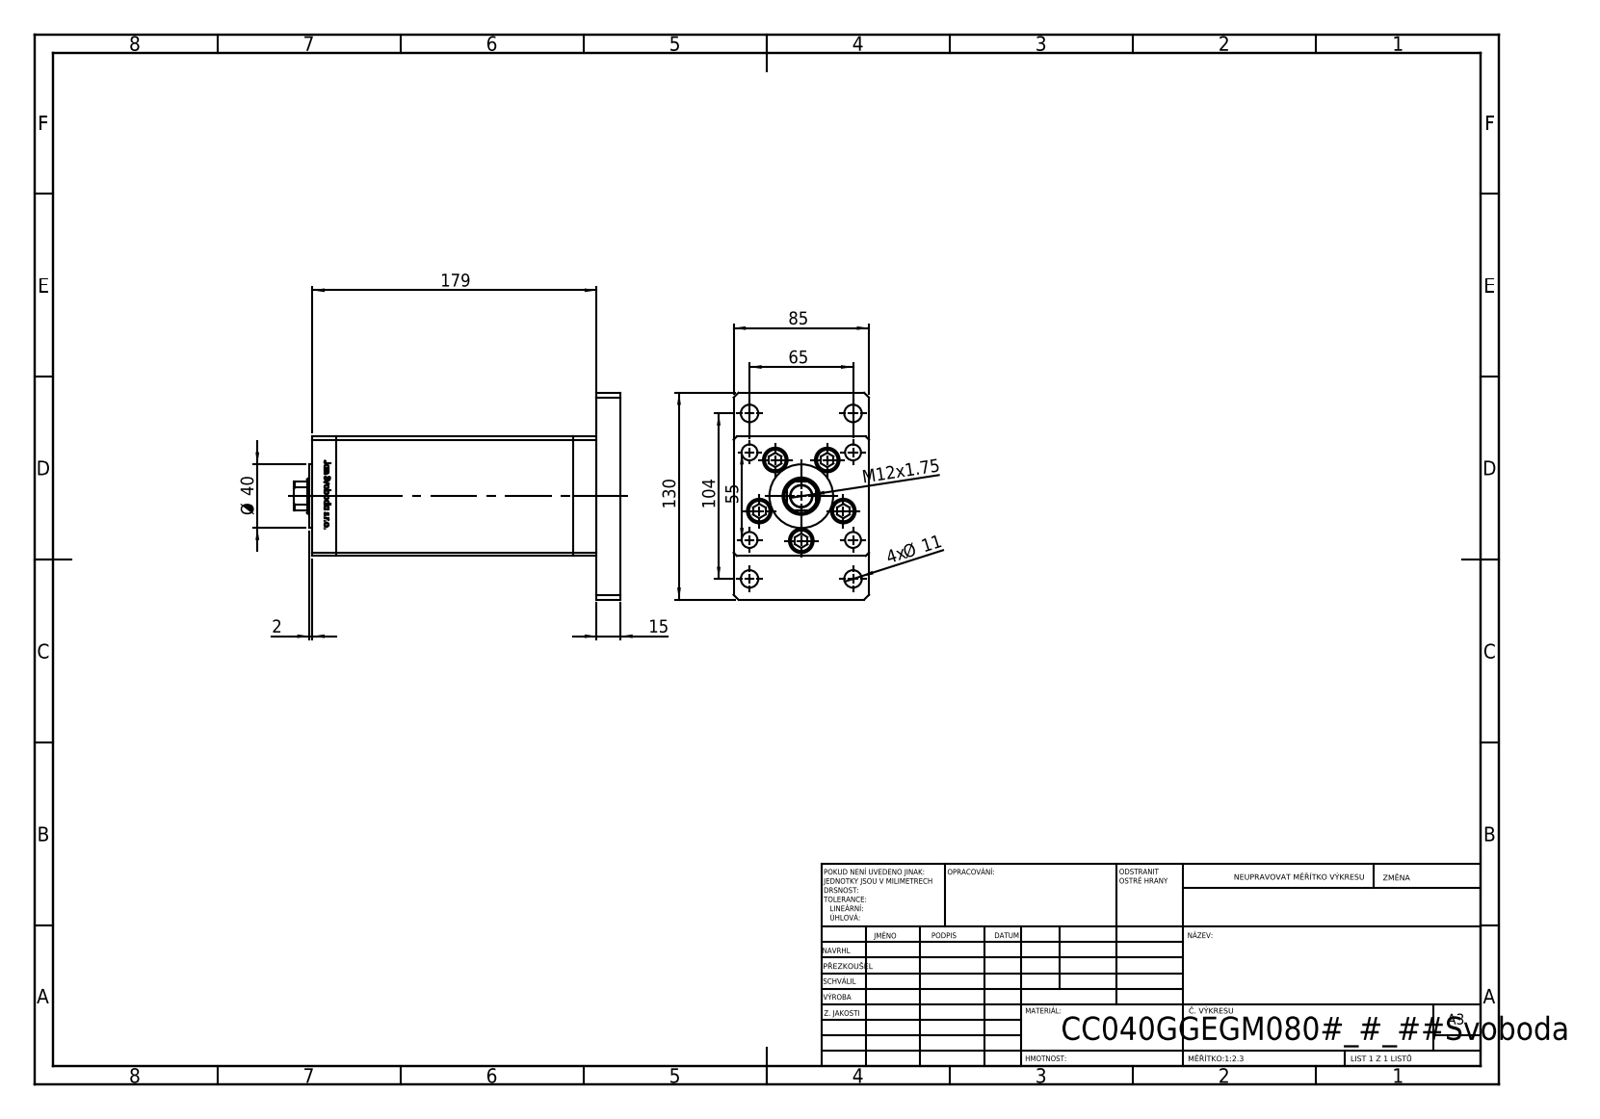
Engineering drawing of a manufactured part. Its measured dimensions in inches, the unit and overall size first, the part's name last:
Units: inches
Overall size (bounding box): 8.071 × 5.118 × 3.346
Round holes (diameter × count): ⌀0.394 ×9, ⌀0.433 ×9, ⌀0.61 ×5, ⌀0.571 ×4, ⌀0.079 ×2, ⌀0.518 ×2, ⌀0.531 ×1, ⌀0.866 ×1, ⌀0.925 ×1, ⌀2.205 ×1
Round bosses / shafts (diameter × count): ⌀0.315 ×9, ⌀0.571 ×5, ⌀1.575 ×1
Partial cylindrical surfaces — rounded edges, fillets, slot ends (radius × count): R0.037 ×2, R0.413 ×1
Main face-to-face distances: 0.591, 3.346, 6.437, 7.028, 2.953, 5.846, 1.181, 0.079, 6.949, 7.618
Hole centre spacings: 1.102, 0.965, 1.676, 2.414, 2.559, 2.735, 3.13, 4.043
Volume: 70.67 in³ · Surface area: 306.2 in²
Bodies: 19 solids, 1313 faces (518 planar, 189 cylindrical, 606 other)
Part name (STEP PRODUCT): V220C_VC_G; V220C_G_MIDDLE; V220C_F; V220C_FRONT_G (+2 more)
STEP written by: SolidWorks 2019 (CONFIG_CONTROL_DESIGN)
